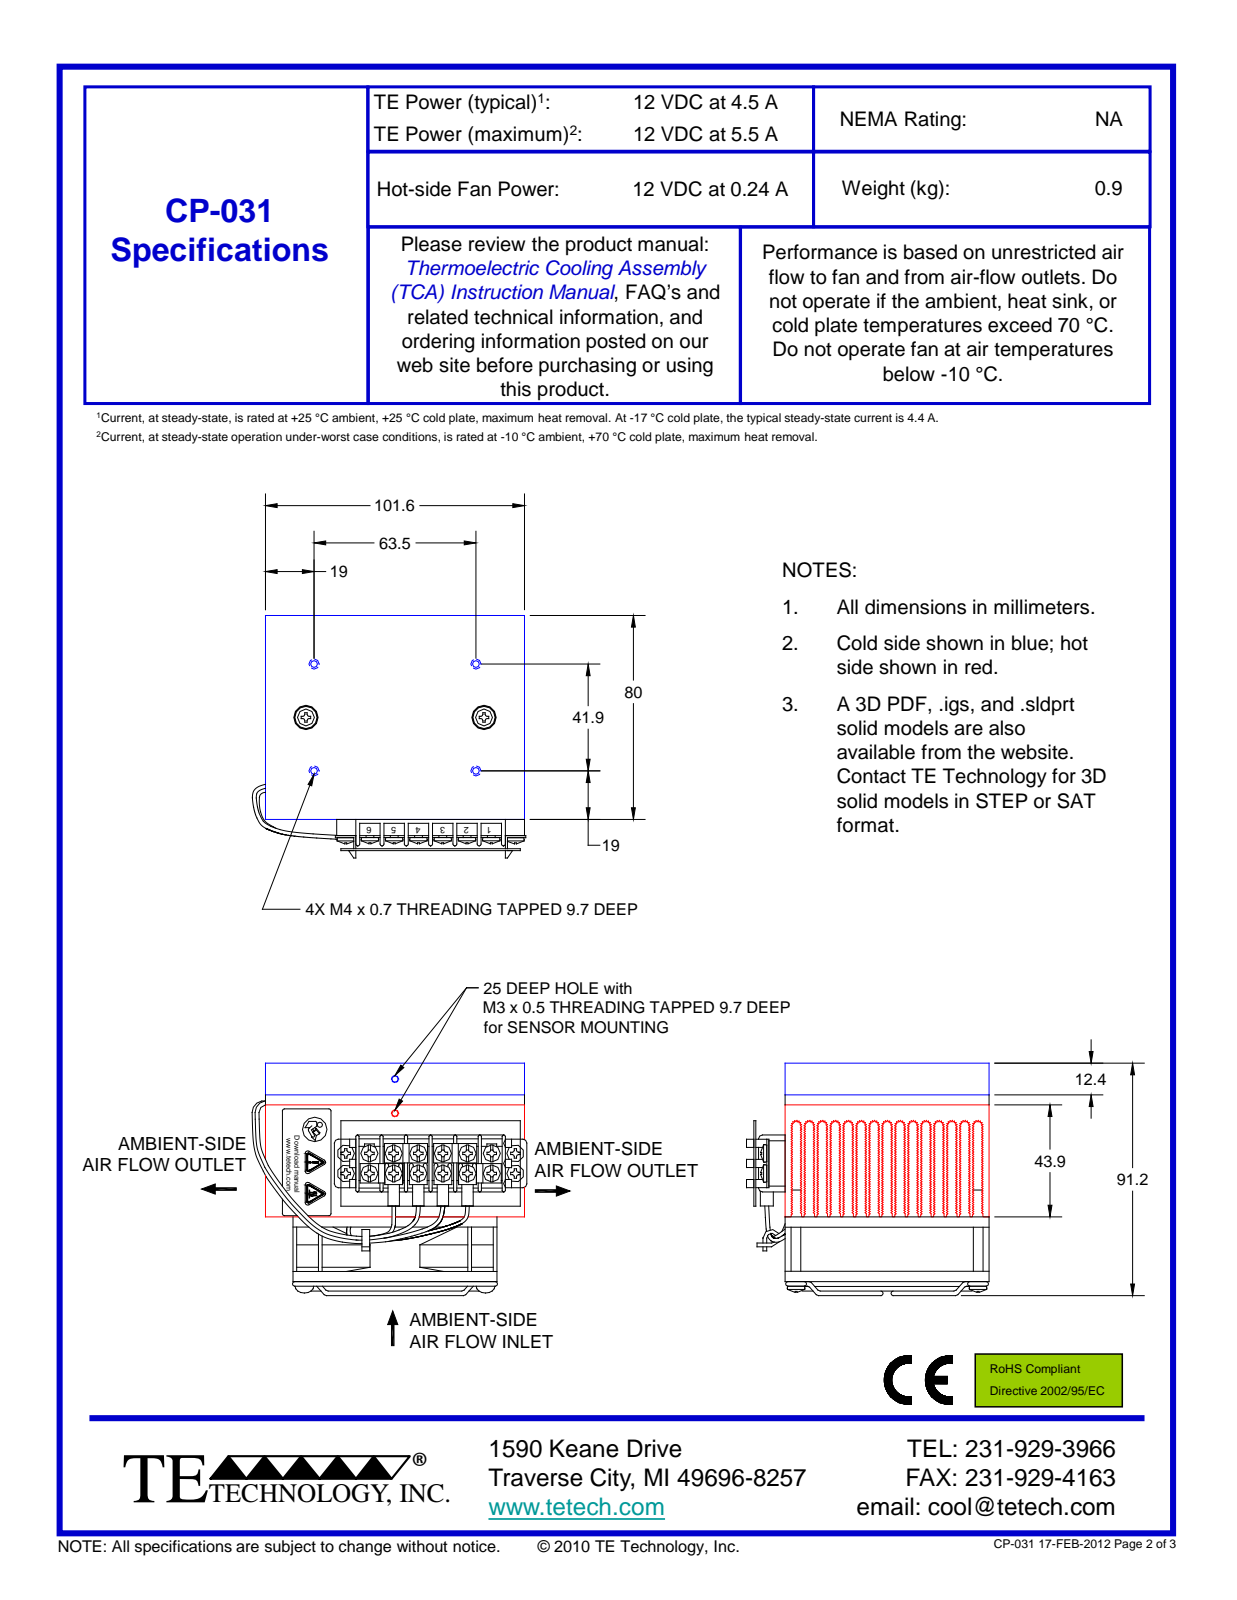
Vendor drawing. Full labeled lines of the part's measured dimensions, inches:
Part name (STEP PRODUCT): 3536 CP-031 gasket; 9A08vvS4021 frame; 9A08vvS4021 hub; 9A08vvS4021 fan (+8 more)
STEP written by: Alibre (AUTOMOTIVE_DESIGN)
Units: inches
Bodies: 119 solids, 2602 faces (1509 planar, 415 cylindrical, 678 other)
Overall size (bounding box): 4.03 × 3.748 × 3.575
Volume: 22.81 in³ · Surface area: 382.5 in²
Round holes (diameter × count): ⌀0.104 ×18, ⌀0.075 ×4, ⌀0.128 ×4, ⌀0.139 ×4, ⌀0.155 ×4, ⌀0.169 ×4, ⌀0.17 ×4, ⌀0.185 ×4, ⌀0.097 ×2, ⌀0.164 ×2, ⌀0.166 ×2, ⌀0.168 ×2
Round bosses / shafts (diameter × count): ⌀0.138 ×18, ⌀0.27 ×16, ⌀0.071 ×9, ⌀0.056 ×9, ⌀0.072 ×6, ⌀0.322 ×4, ⌀0.295 ×4, ⌀0.193 ×4
Partial cylindrical surfaces — rounded edges, fillets, slot ends (radius × count): R0.01 ×34, R0.038 ×21, R0.031 ×16, R0.015 ×8, R0.03 ×8, R0.031 ×8, R0.032 ×8, R0.078 ×8
Main face-to-face distances: 0.2, 0.4, 0.6, 0.8, 1, 1.2, 1.4, 1.6, 1.8, 0.154
Hole centre spacings: 0.75, 0.31, 0.812, 0.375, 0.375, 0.487, 0.835, 1.408
